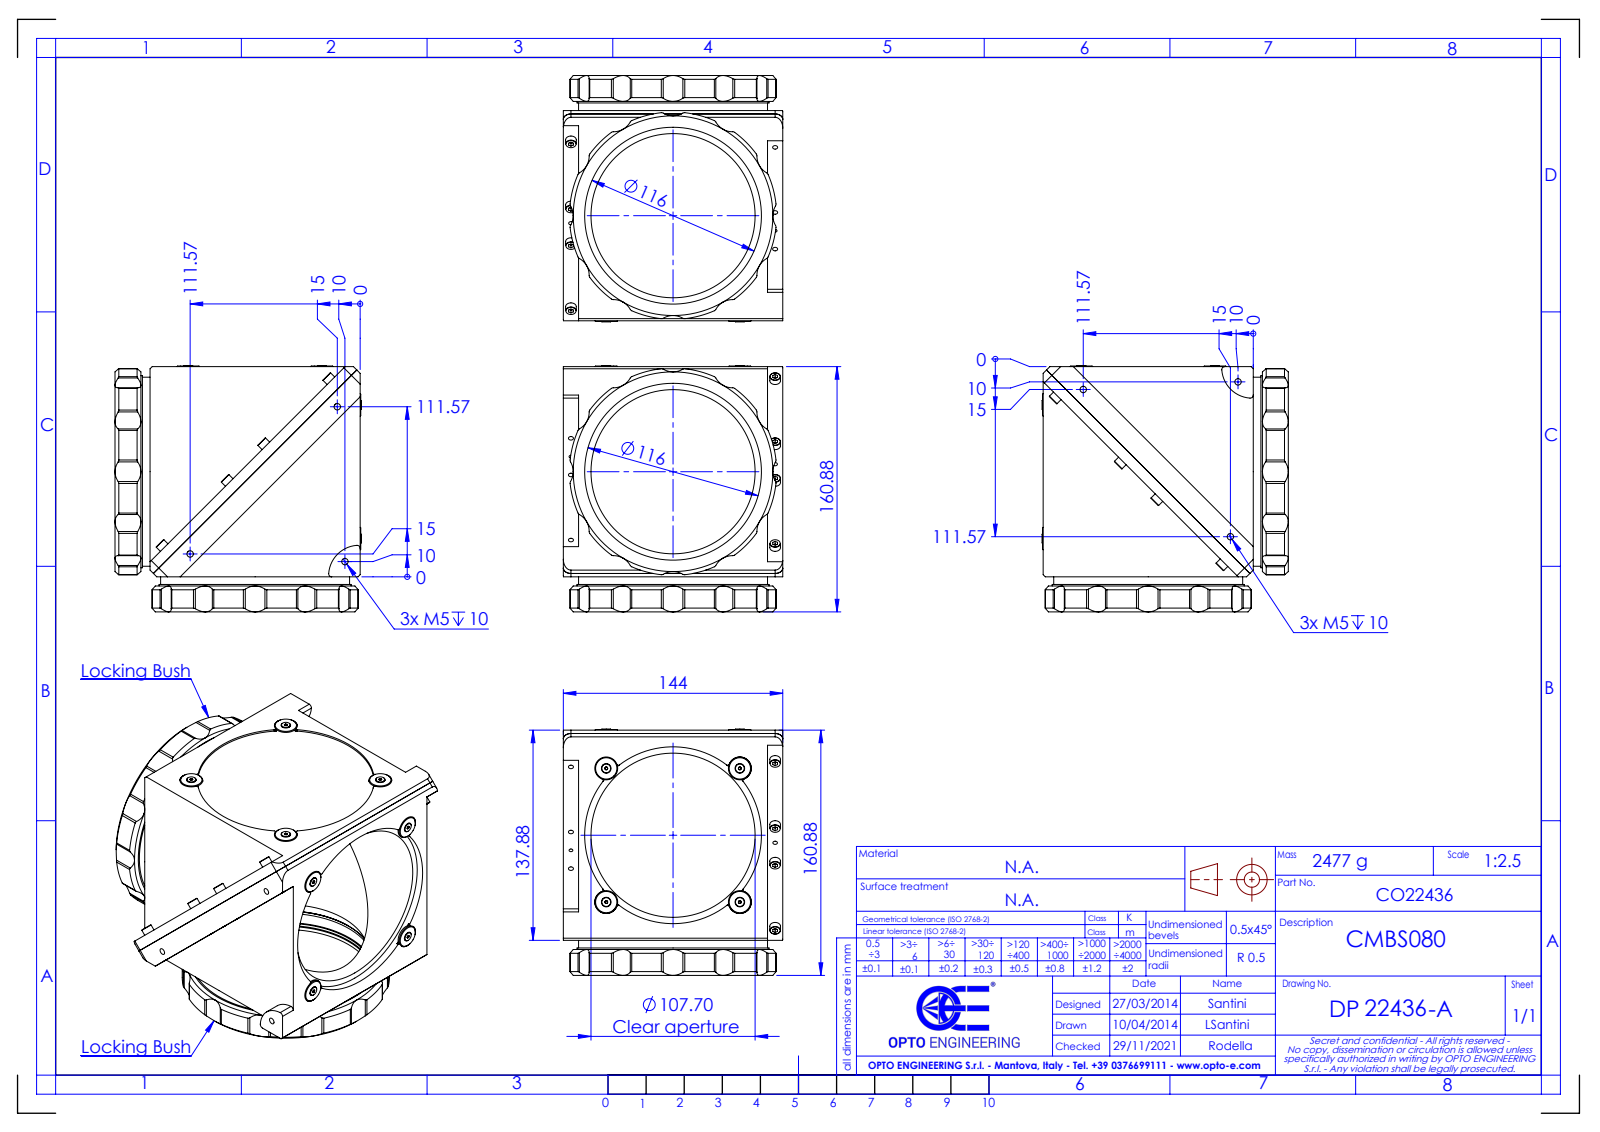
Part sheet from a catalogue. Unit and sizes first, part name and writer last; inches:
Units: inches
Overall size (bounding box): 6.363 × 6.363 × 5.669
Round holes (diameter × count): ⌀0.13 ×8, ⌀0.165 ×6, ⌀0.591 ×4, ⌀0.098 ×2, ⌀0.118 ×2, ⌀4.24 ×2, ⌀4.567 ×2, ⌀4.591 ×2, ⌀4.654 ×2, ⌀4.724 ×2, ⌀4.882 ×2
Round bosses / shafts (diameter × count): ⌀0.276 ×8, ⌀0.226 ×8, ⌀0.591 ×4, ⌀4.961 ×2, ⌀4.551 ×1
Partial cylindrical surfaces — rounded edges, fillets, slot ends (radius × count): R0.079 ×52, R0.492 ×24, R0.039 ×16, R0.197 ×4, R0.787 ×2, R2.677 ×2
Main face-to-face distances: 0.079, 4.882, 5.428, 0.157, 0.197, 0.394, 5.276, 5.231, 0.276, 0.039
Hole centre spacings: 5.276, 0.669, 2.377, 2.441, 3.046, 3.715, 4.004, 4.49
Bodies: 0 solids, 583 faces (149 planar, 298 cylindrical, 136 other)
Part name (STEP PRODUCT): DP22436 -A_CMBS080
STEP written by: SolidWorks 2021 (CONFIG_CONTROL_DESIGN)
